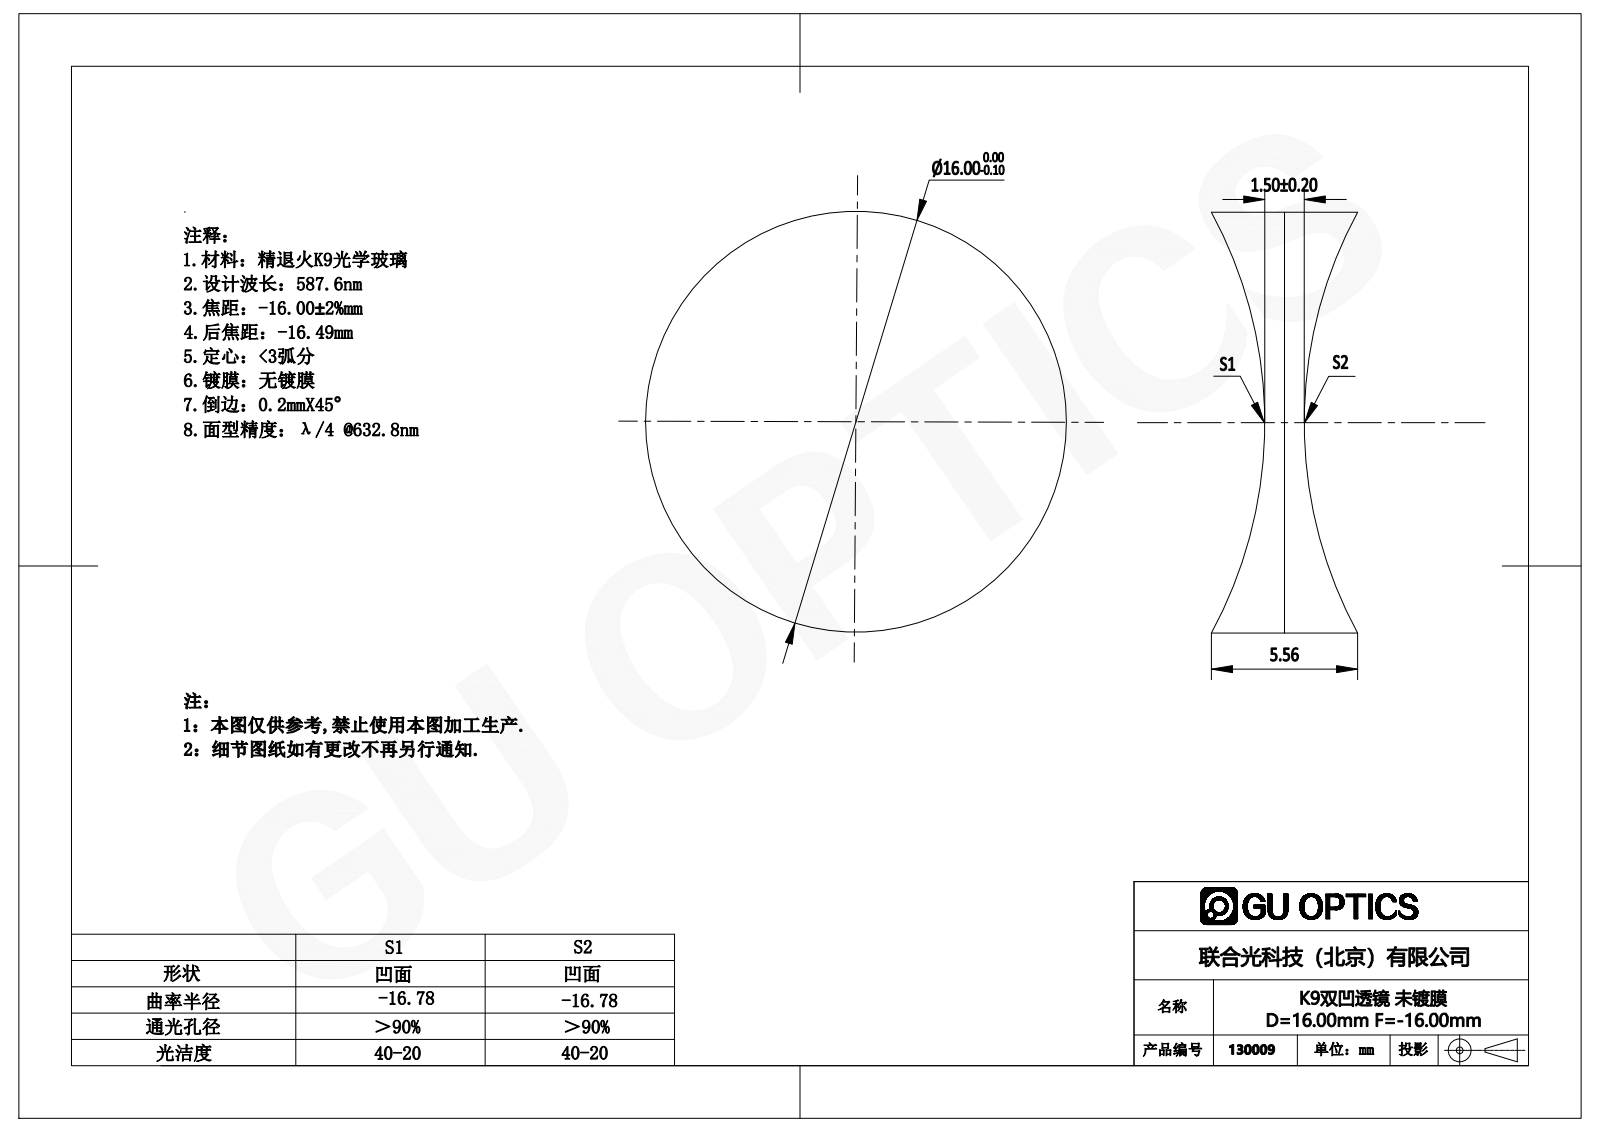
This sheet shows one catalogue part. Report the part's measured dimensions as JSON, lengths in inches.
{"part_name": "130009", "step_written_by": "SolidWorks 2016 (AUTOMOTIVE_DESIGN)", "units": "inches", "bodies": {"solids": 1, "faces": 6, "planar": 0, "cylindrical": 2, "other": 4}, "overall_size": [0.63, 0.63, 0.219], "volume_in3": 0.043, "surface_area_in2": 1.1, "round_bosses_or_shafts": [[0.63, 1]]}
